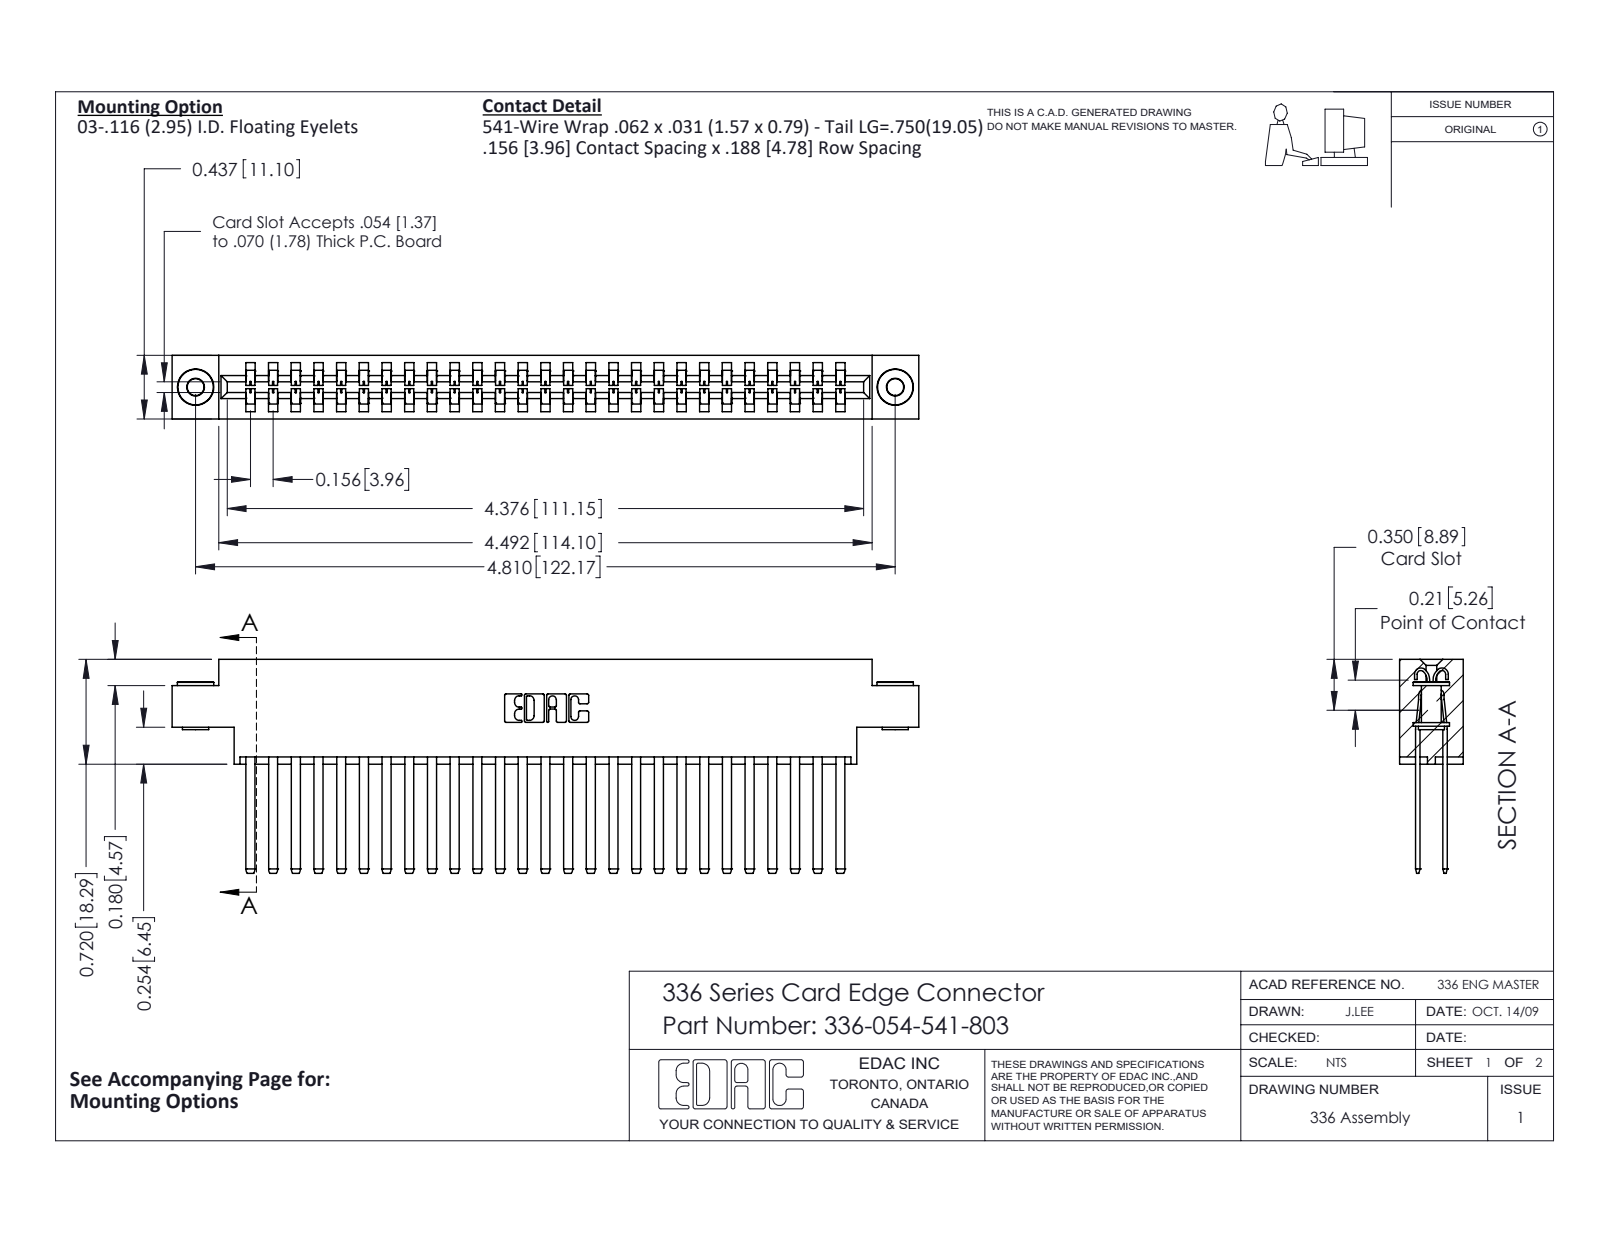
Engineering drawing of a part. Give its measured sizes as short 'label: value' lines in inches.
name: 345-250-002_345-250-002-102; 336-054-541-803; 336-290-001_336-290-541; 336 Part_Offset - .156 Dia - TH
written by: SolidWorks 2020 (CONFIG_CONTROL_DESIGN)
unit: in
bodies: 57 solids, 2424 faces (1488 planar, 928 cylindrical, 8 other)
size: 5.133 × 1.47 × 0.437
volume: 1.201 in³; area: 39.03 in²
holes: 2× ⌀0.116, 2× ⌀0.156
bosses: 2× ⌀0.25, 2× ⌀0.18, 2× ⌀0.136
rounds: 108× R0.004, 54× R0.056, 22× R0.01, 6× R0.007, 6× R0.031, 4× R0.022, 4× R0.04, 3× R0.026
face distances: 0.188, 0.031, 0.328, 0.14, 0.297, 0.109, 0.437, 0.033, 0.181, 0.256
hole spacings: 4.81
